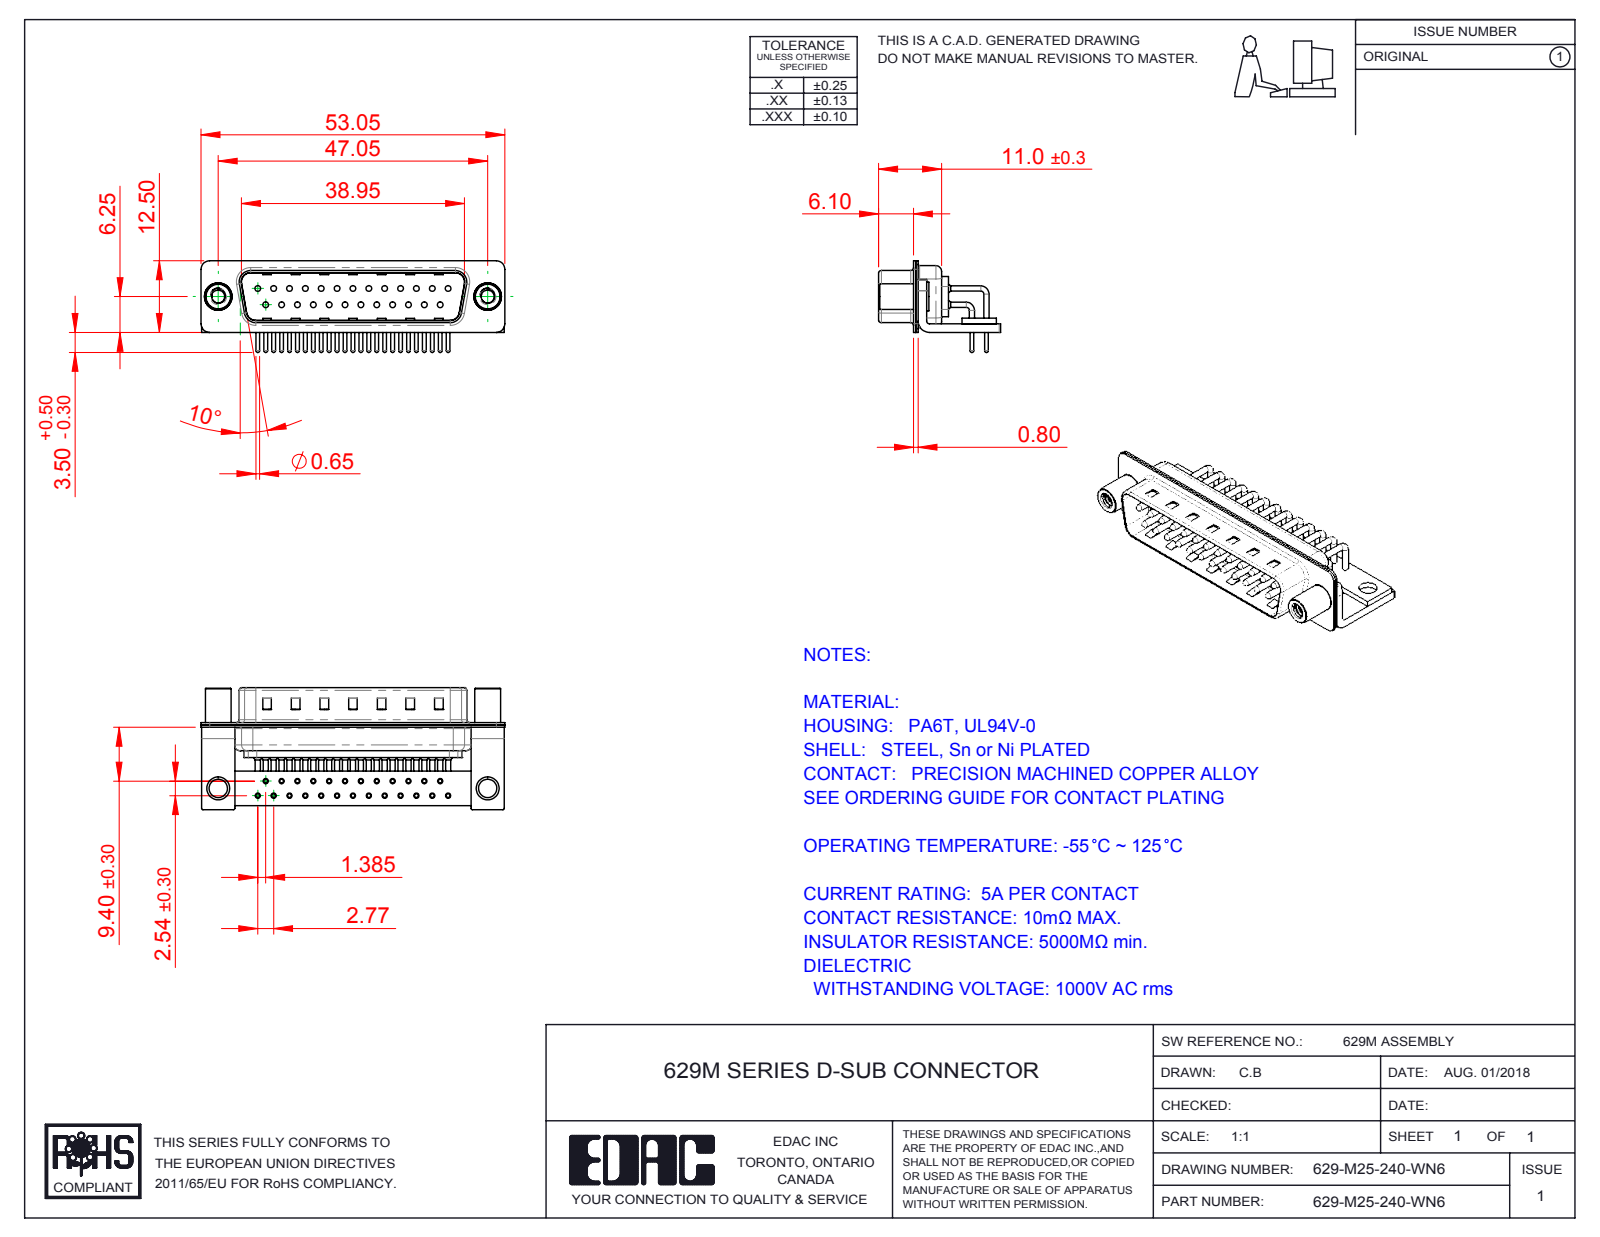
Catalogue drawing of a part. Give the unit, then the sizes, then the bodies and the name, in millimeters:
Units: millimetres
Overall size (bounding box): 53.05 × 21.3 × 16
Round holes (diameter × count): ⌀0.9 ×25, ⌀1 ×25, ⌀1.7 ×25, ⌀2 ×25, ⌀2.26 ×2, ⌀3.2 ×2, ⌀4 ×2, ⌀4.8 ×2
Round bosses / shafts (diameter × count): ⌀1.5 ×25, ⌀0.9 ×25, ⌀0.65 ×25, ⌀5 ×2, ⌀4.9 ×2, ⌀4.5 ×2
Partial cylindrical surfaces — rounded edges, fillets, slot ends (radius × count): R1.01 ×25, R0.25 ×16, R1.5 ×16, R2 ×13, R0.5 ×9, R1.6 ×8, R0.6 ×4, R0.65 ×4
Main face-to-face distances: 0.4, 0.85, 1.25, 1.5, 9.55, 0.8, 10.4, 8.3, 1, 1.9
Hole centre spacings: 2.77, 5.54, 8.31, 11.08, 13.85, 3.16, 4.87, 16.62
Volume: 3 592 mm³ · Surface area: 9 451 mm²
Bodies: 33 solids, 3276 faces (1799 planar, 1151 cylindrical, 326 other)
Part name (STEP PRODUCT): 629M Shell Front_25 Contacts; 629M Housing_25 Contacts; 629M Shell Rear_25 Contacts; 629M Contact Row 1 (+5 more)
STEP written by: SolidWorks 2016 (CONFIG_CONTROL_DESIGN)
